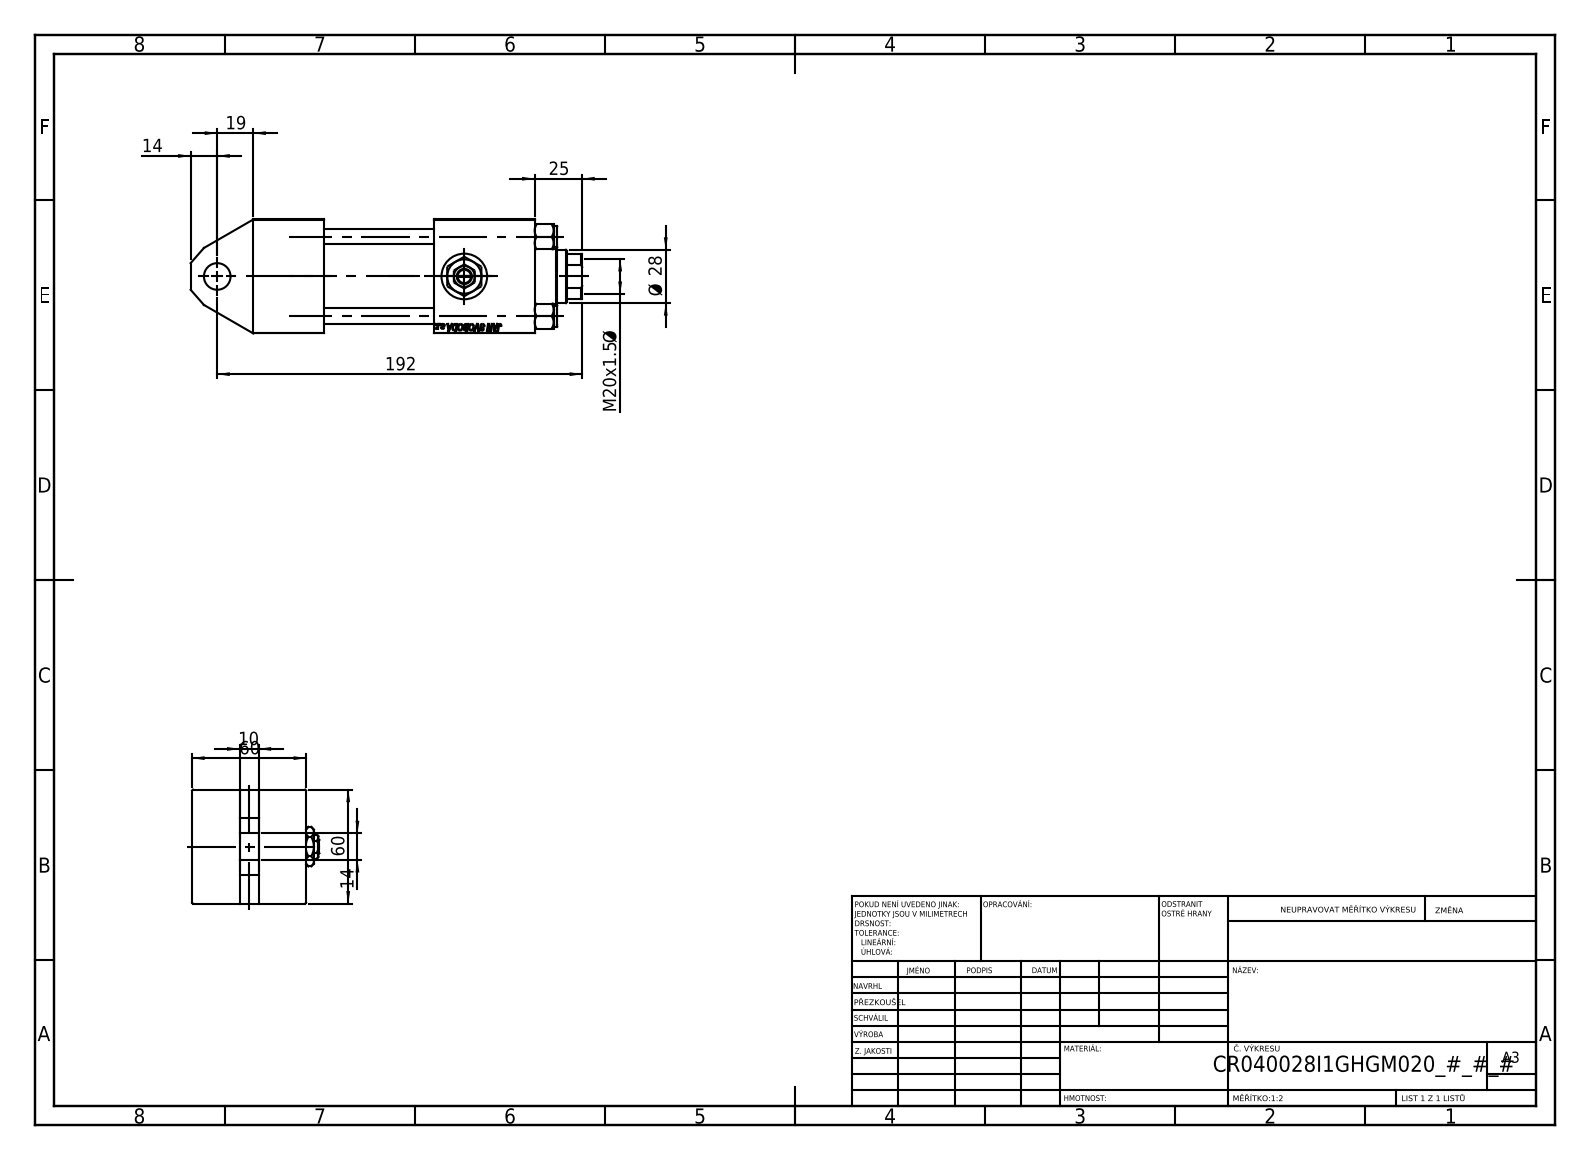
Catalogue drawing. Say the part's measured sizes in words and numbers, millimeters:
The part is named "V215CR_VCP_I; Zatka_pro_OIL_PORT; V215CR_TYCINKA_I; V215_VC_A (+2 more)". Its 3-D file was written by "SolidWorks 2019 (CONFIG_CONTROL_DESIGN)". It is 12 solids with 1127 faces: 526 planar, 85 cylindrical and 516 other. Overall it measures 206 by 67 by 60 millimeters. Its volume is 437 965 cubic millimeters and its surface area 116 949 square millimeters. Round holes: 4 of diameter 8, 2 of diameter 7, 2 of diameter 16.66, 2 of diameter 24, 1 of diameter 14, 1 of diameter 18.5, 1 of diameter 28, 1 of diameter 31, 1 of diameter 40, 1 of diameter 45. Round bosses or shafts: 4 of diameter 11, 1 of diameter 46, 1 of diameter 42. Partial cylindrical surfaces (rounded edges, fillets, slot ends): 1 of radius 13.5. The main face-to-face distances are 60, 37, 25, 53, 58, 35, 95, 148, 111, 119.3. The hole center spacings are 29.49, 41.7, 58.97, 37.5, 92.5, 130.
